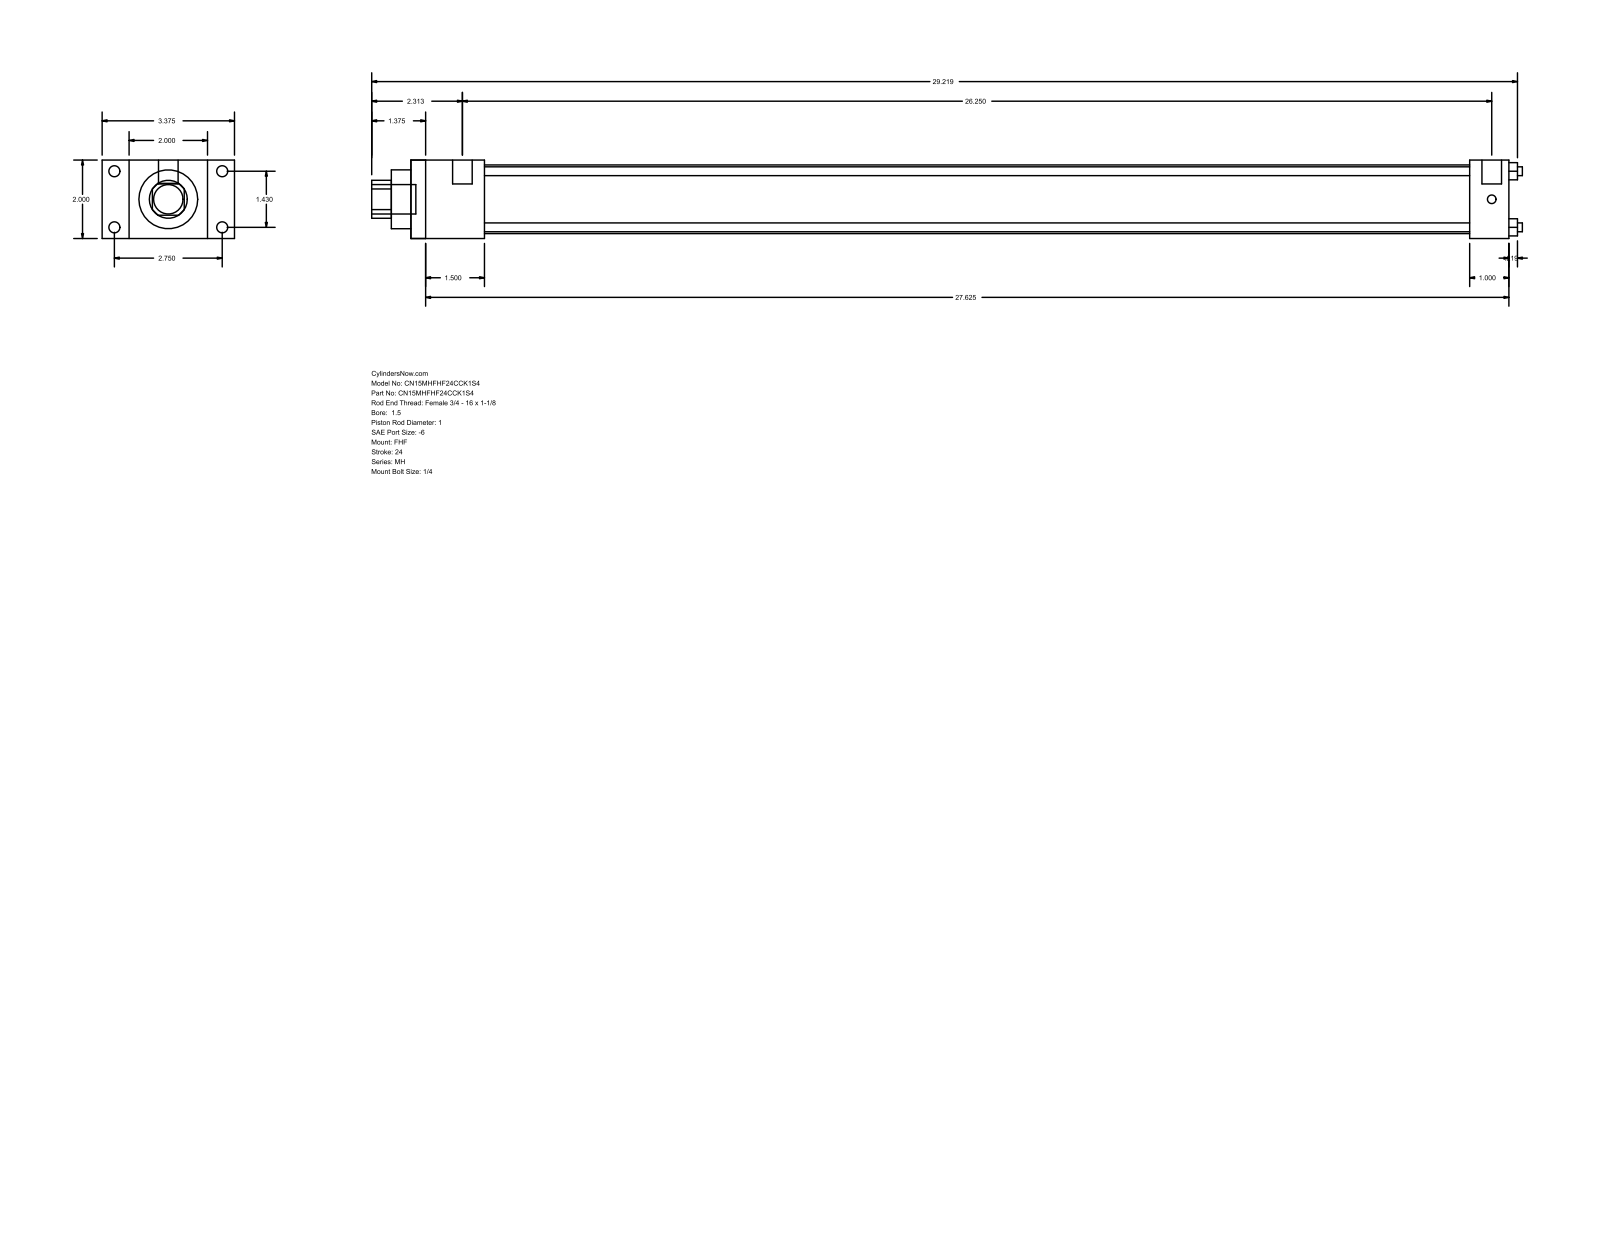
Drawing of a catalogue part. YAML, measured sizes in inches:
part_name: "MH_FHF__0150_1"
step_written_by: "GSSL Pune (CONFIG_CONTROL_DESIGN)"
units: inches
bodies: {solids: 0, faces: 88, planar: 60, cylindrical: 28, other: 0}
overall_size: [29.344, 3.375, 2]
round_holes:
  - {diameter: 0.225, count: 4}
  - {diameter: 1, count: 1}
  - {diameter: 1.5, count: 1}
  - {diameter: 1.75, count: 1}
round_bosses_or_shafts:
  - {diameter: 0.281, count: 4}
  - {diameter: 0.219, count: 4}
  - {diameter: 0.5, count: 2}
  - {diameter: 0.75, count: 1}
partial_cylinders:
  - {radius: 0.484, count: 1}
face_to_face_distances: [2, 0.687, 2.687, 1.875, 3.375, 28, 26.125, 1, 27, 25.125]
hole_center_spacings: [1.011, 1.43, 2.022]
